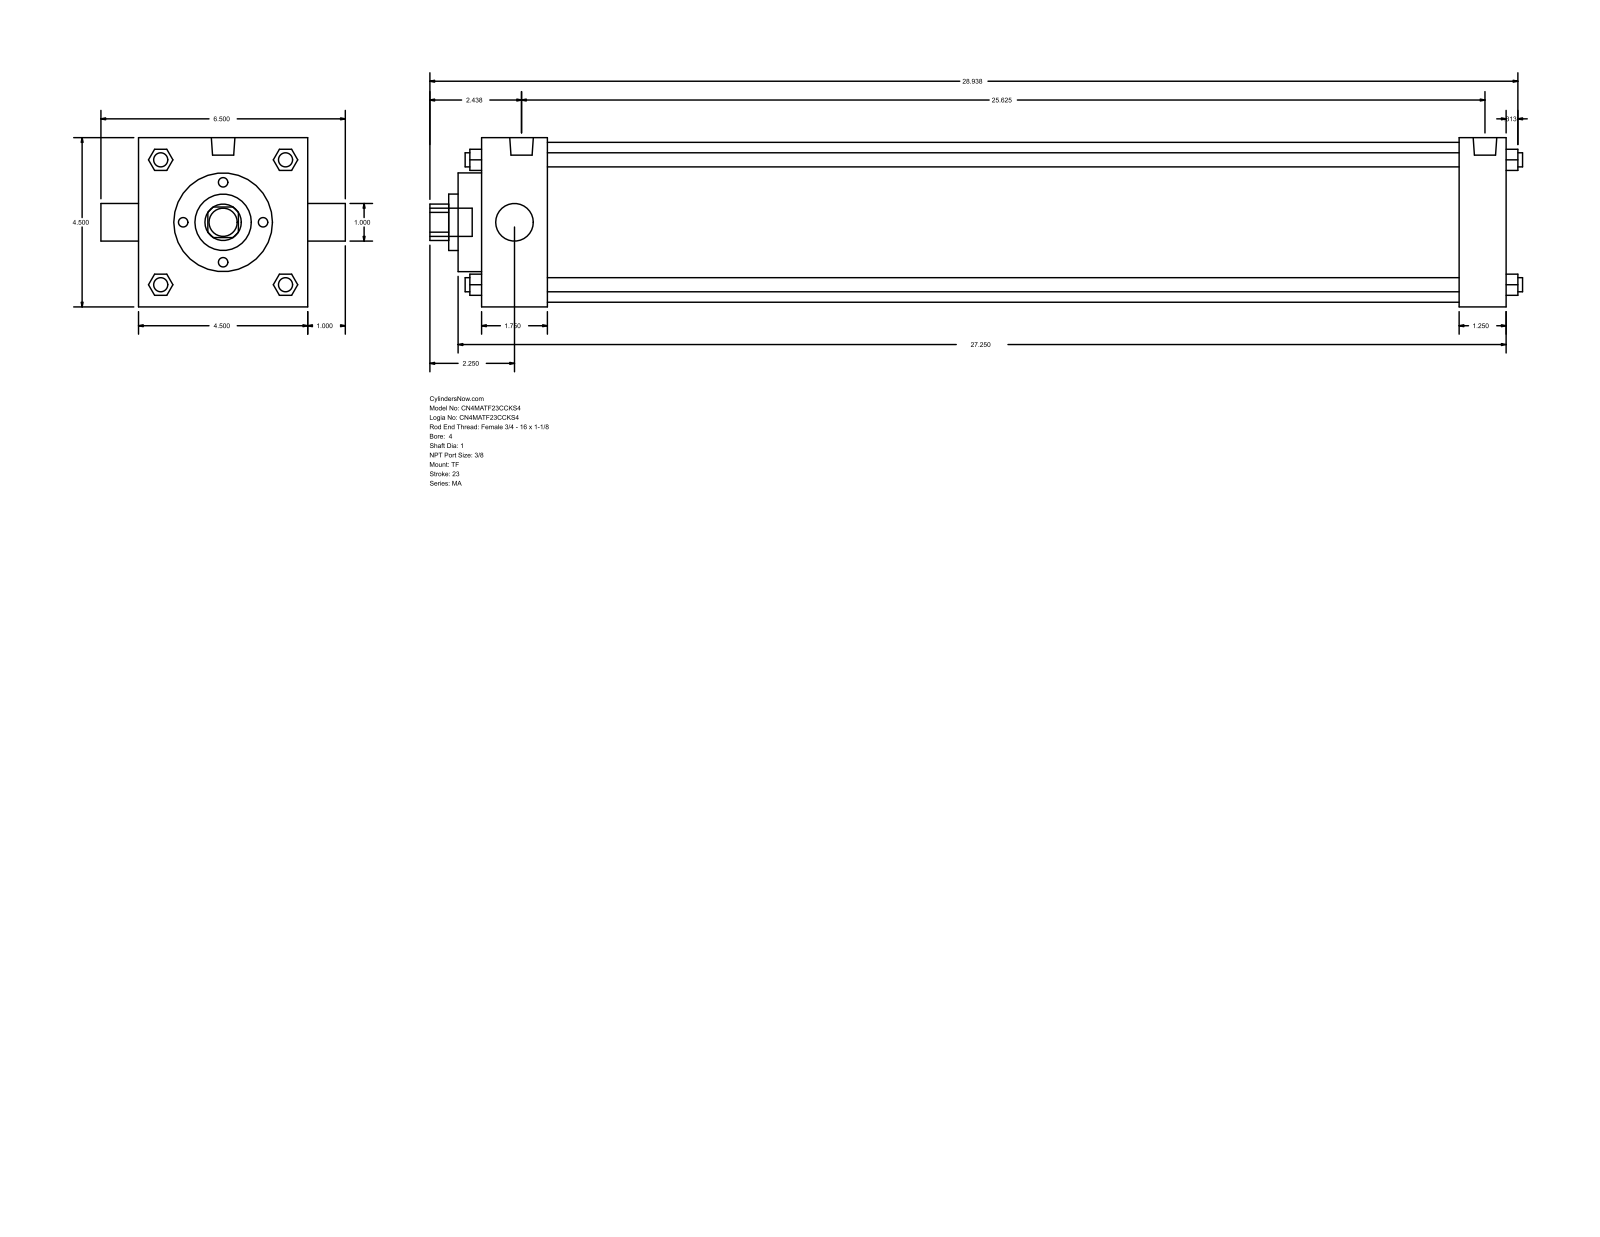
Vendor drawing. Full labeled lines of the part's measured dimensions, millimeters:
Part name (STEP PRODUCT): MA_TF__0400_1
STEP written by: GSSL Pune (CONFIG_CONTROL_DESIGN)
Units: millimetres
Bodies: 0 solids, 122 faces (93 planar, 29 cylindrical, 0 other)
Overall size (bounding box): 738.19 × 165.1 × 114.3
Round holes (diameter × count): ⌀25.4 ×2, ⌀38.1 ×1, ⌀66.67 ×1, ⌀107.95 ×1
Round bosses / shafts (diameter × count): ⌀9.53 ×4, ⌀11.11 ×3, ⌀15.93 ×2, ⌀19.05 ×1
Partial cylindrical surfaces — rounded edges, fillets, slot ends (radius × count): R12.29 ×1
Main face-to-face distances: 114.3, 692.16, 660.41, 31.75, 44.46, 615.95, 647.7, 15.87, 60.33, 676.28
